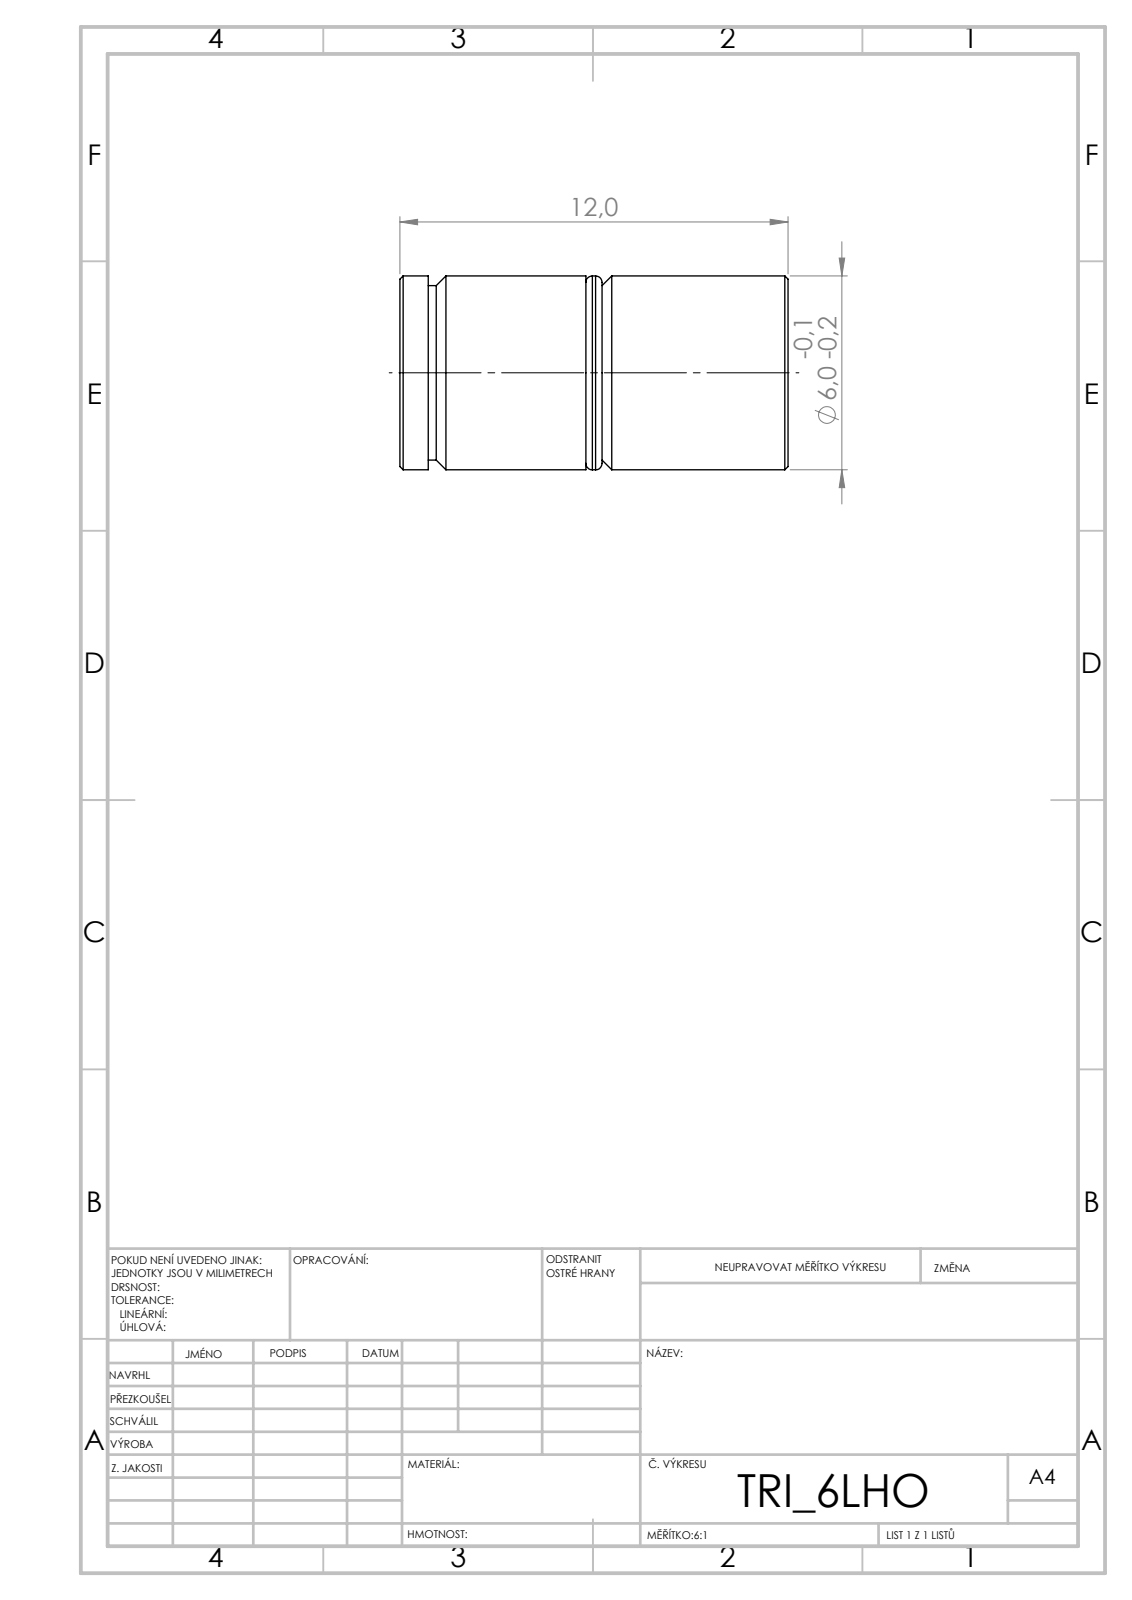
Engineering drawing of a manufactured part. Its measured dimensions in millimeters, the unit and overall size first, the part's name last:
Units: millimetres
Overall size (bounding box): 12 × 6 × 6
Round bosses / shafts (diameter × count): ⌀6 ×1, ⌀5.4 ×1
Main face-to-face distances: 5.75, 6.25, 0.5, 4.75, 5.25, 11, 1, 12, 4.2, 11.13
Volume: 332 mm³ · Surface area: 369 mm²
Bodies: 2 solids, 43 faces (19 planar, 12 cylindrical, 12 other)
STEP written by: SolidWorks 2019 (CONFIG_CONTROL_DESIGN)
